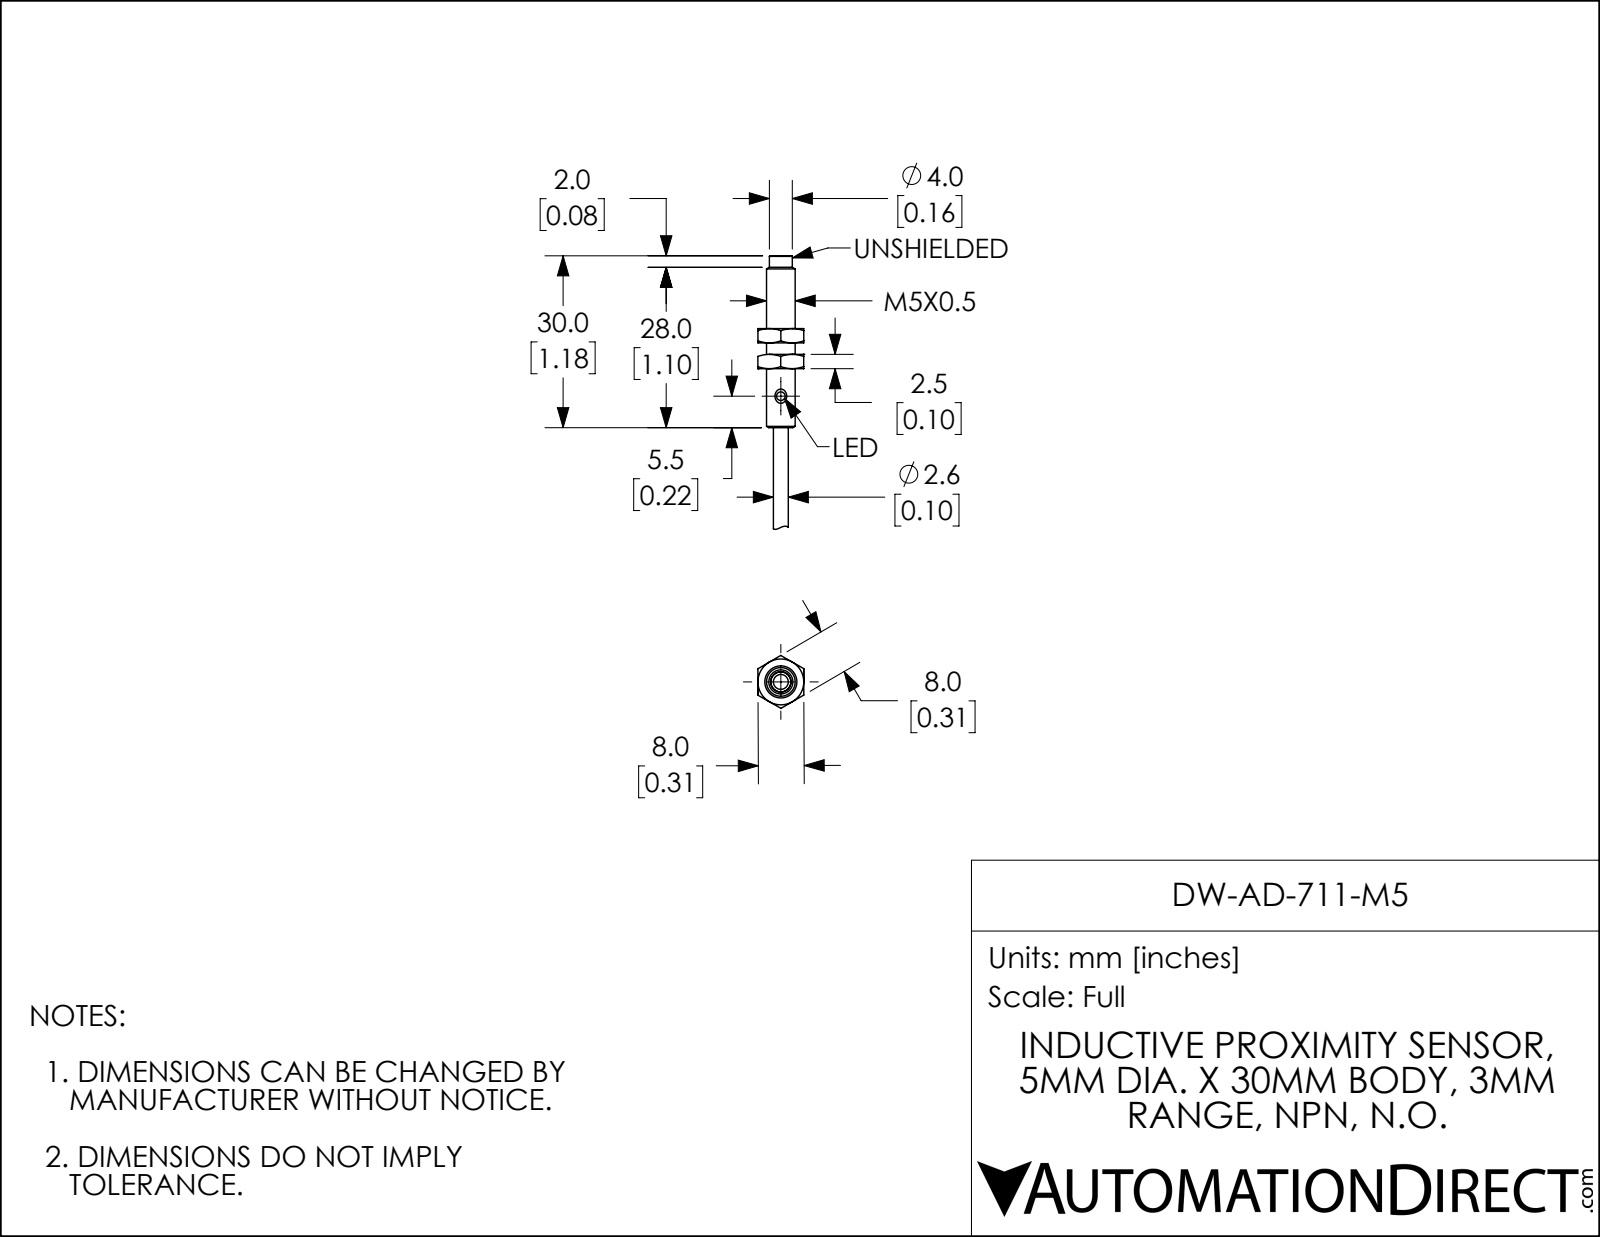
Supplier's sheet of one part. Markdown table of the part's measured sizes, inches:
| quantity | value |
| --- | --- |
| part name | DW-AD-711-M5 |
| STEP written by | SolidWorks 2018 (AUTOMOTIVE_DESIGN) |
| units | inches |
| bodies | 1 solid, 13 faces (2 planar, 5 cylindrical, 6 other) |
| overall size | 1.887 × 0.197 × 0.197 |
| volume | 0.045 in³ |
| surface area | 1.074 in² |
| round holes (diameter × count) | 0.059 × 1 |
| round bosses / shafts (diameter × count) | 0.197 × 1, 0.157 × 1, 0.138 × 1 |
| main face-to-face distances | 1.181 |
